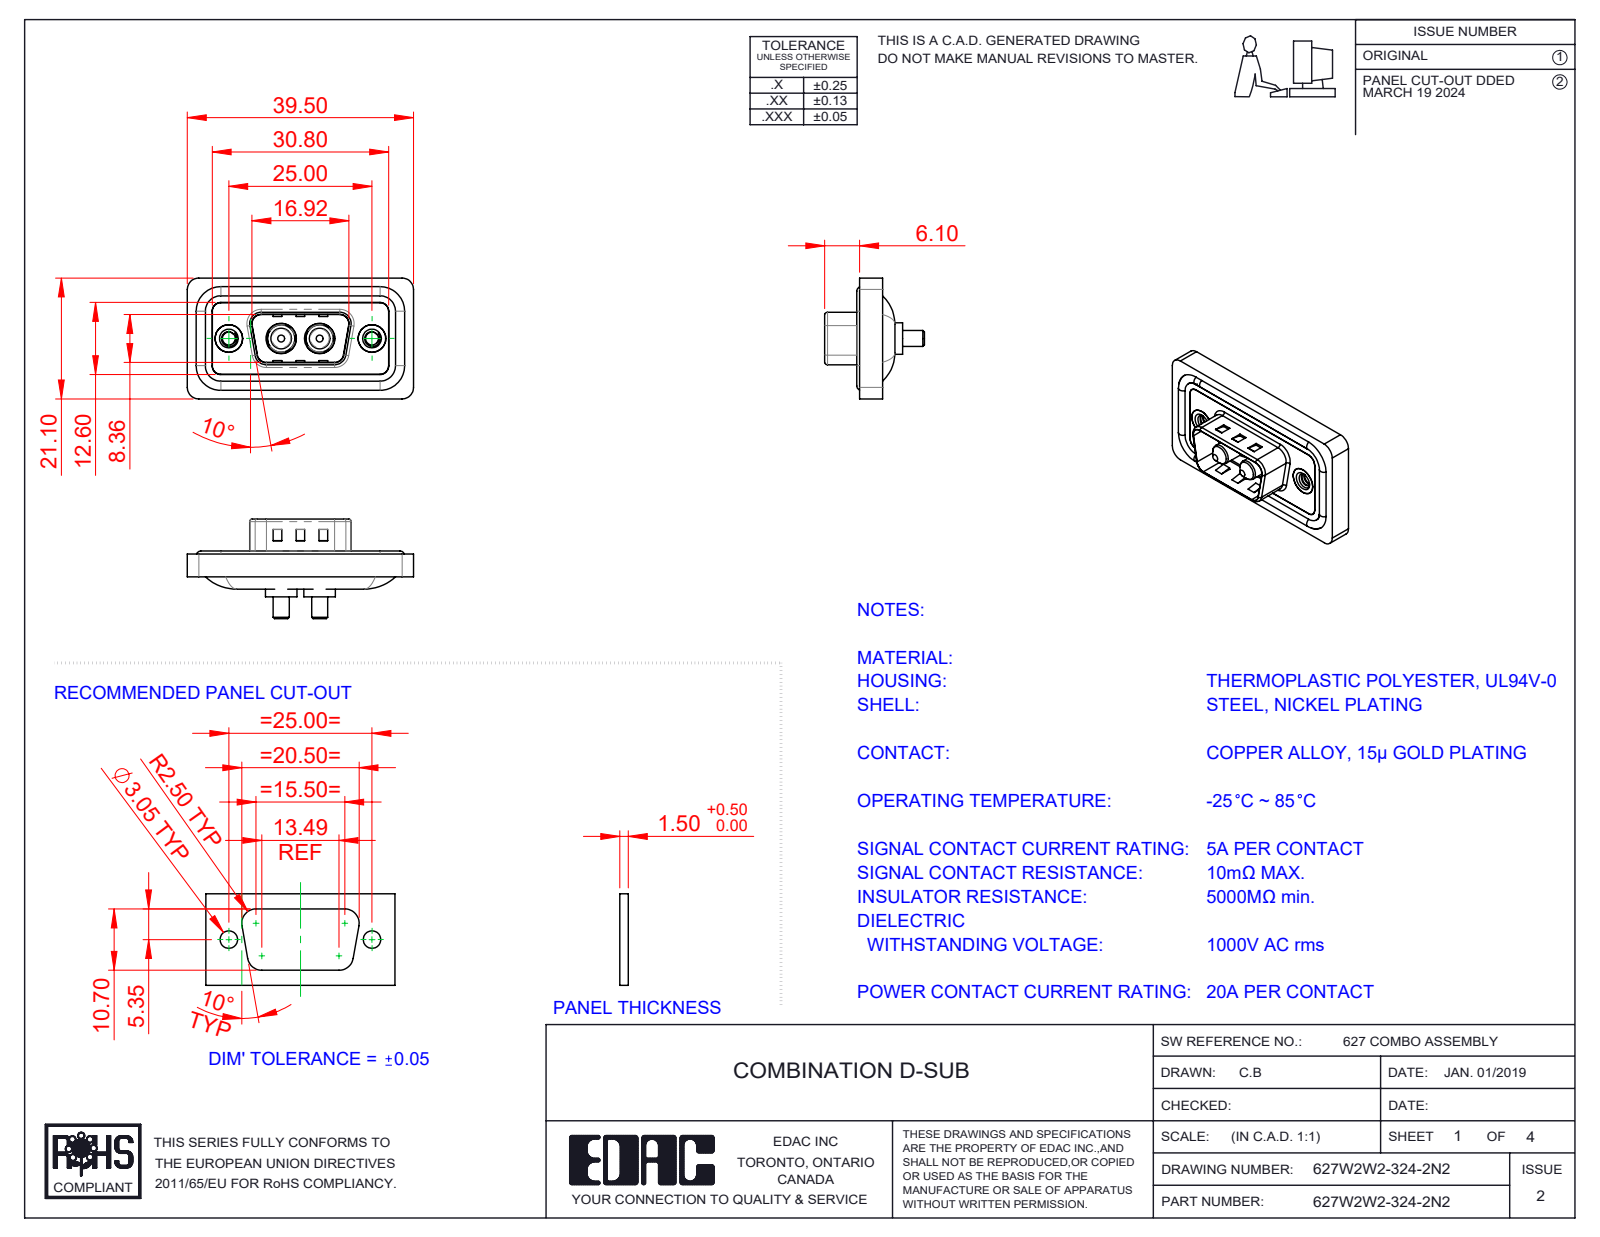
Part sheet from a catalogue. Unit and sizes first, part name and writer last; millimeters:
Units: millimetres
Overall size (bounding box): 39.5 × 21.1 × 17.4
Round holes (diameter × count): ⌀2.26 ×2, ⌀4 ×2, ⌀4.8 ×2, ⌀4.85 ×2, ⌀5 ×2, ⌀5.3 ×2
Round bosses / shafts (diameter × count): ⌀1.6 ×4, ⌀5.5 ×2, ⌀5.2 ×2, ⌀4.9 ×2, ⌀4.75 ×2, ⌀3.75 ×2, ⌀3.6 ×2, ⌀2.8 ×2
Partial cylindrical surfaces — rounded edges, fillets, slot ends (radius × count): R1.5 ×22, R2 ×18, R0.5 ×8, R1.6 ×8, R0.25 ×4, R0.6 ×4, R0.65 ×4, R0.9 ×4
Main face-to-face distances: 0.4, 1.1, 2.9, 3.1, 0.5, 1.6, 1.5, 4, 2.5, 0.7
Hole centre spacings: 9.14, 15.86, 6.72, 25
Volume: 4 460 mm³ · Surface area: 6 984 mm²
Bodies: 11 solids, 489 faces (165 planar, 218 cylindrical, 106 other)
Part name (STEP PRODUCT): 627Combo Housing_2W2; Power Pin_20A S; 627Combo Shell Rear_09 Contacts; 627Combo Shell Front_09 Contacts (+3 more)
STEP written by: SolidWorks 2023 (CONFIG_CONTROL_DESIGN)
